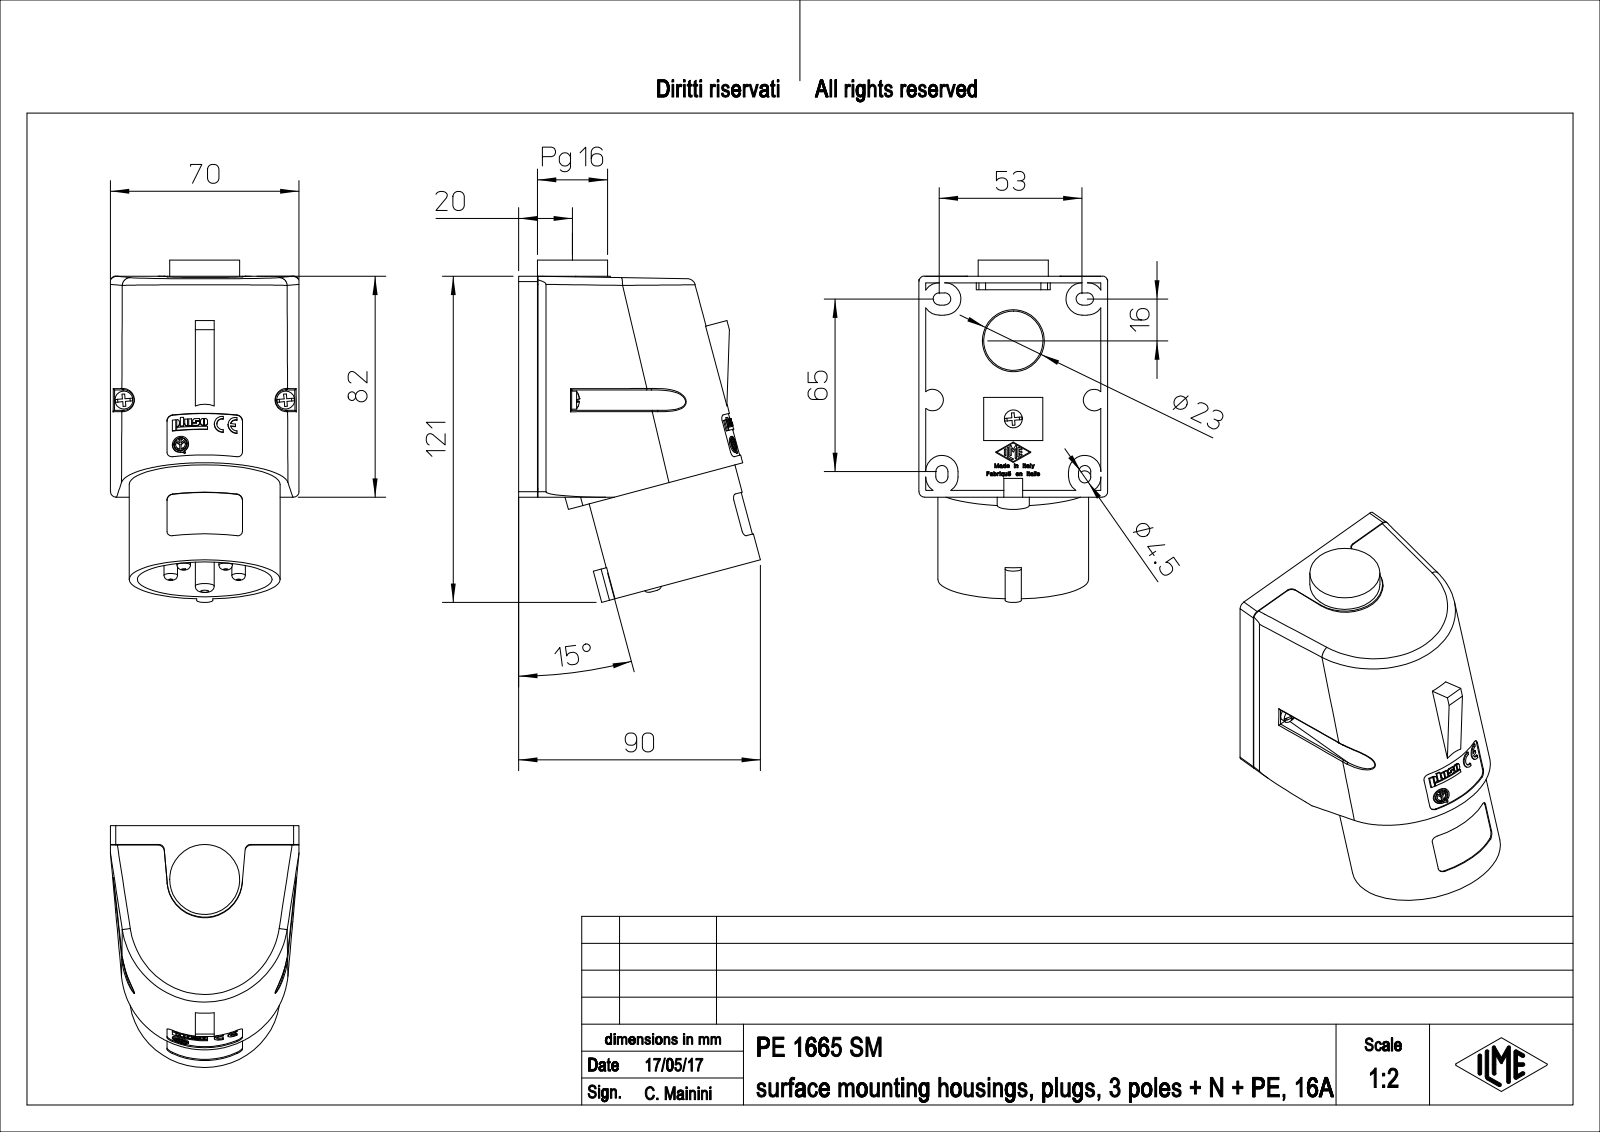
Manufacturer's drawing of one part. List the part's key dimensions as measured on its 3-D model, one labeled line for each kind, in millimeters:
Part name (STEP PRODUCT): PE_1665_SM
STEP written by: PTC Creo Elements/Direct Modeling 19.0E 27-Jun-2016 (C) Parametric Technology GmbH (AUTOMOTIVE_DESIGN)
Units: millimetres
Bodies: 1 solid, 1845 faces (1561 planar, 188 cylindrical, 96 other)
Overall size (bounding box): 127.04 × 89.75 × 70
Volume: 341 934 mm³ · Surface area: 67 379 mm²
Round holes (diameter × count): ⌀3.2 ×2, ⌀4.3 ×2, ⌀4.5 ×2, ⌀3 ×1, ⌀5.04 ×1, ⌀21.3 ×1, ⌀23 ×1, ⌀24 ×1, ⌀50 ×1
Round bosses / shafts (diameter × count): ⌀5 ×6, ⌀6.7 ×5, ⌀26 ×2, ⌀56 ×1, ⌀49 ×1, ⌀7 ×1, ⌀6 ×1
Partial cylindrical surfaces — rounded edges, fillets, slot ends (radius × count): R0.25 ×15, R2 ×14, R6 ×13, R0.5 ×9, R0.86 ×9, R2.25 ×8, R4 ×8, R1 ×6
Main face-to-face distances: 2.5, 6.2, 3.7, 3.5, 6, 1, 7.2, 7, 82, 3
Hole centre spacings: 37.2, 60
